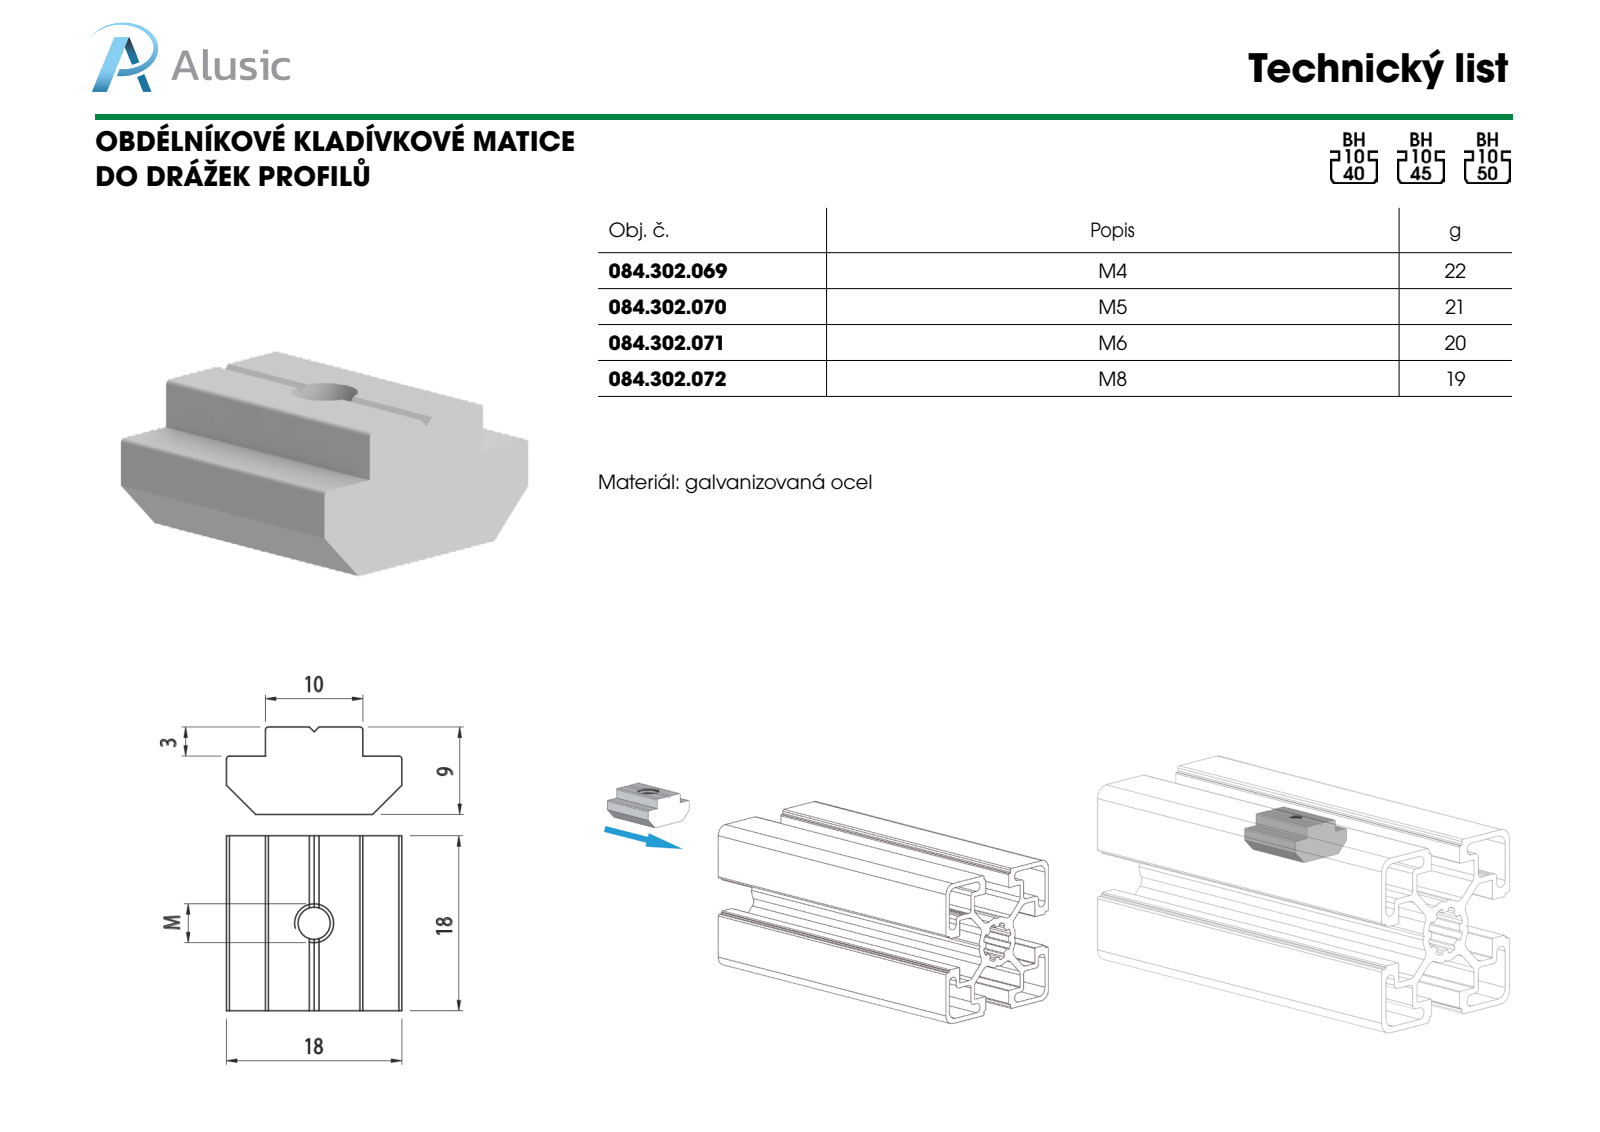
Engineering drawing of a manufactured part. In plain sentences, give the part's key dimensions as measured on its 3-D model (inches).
The part is named "084.302.069". Its 3-D file was written by "SolidWorks 2012 (CONFIG_CONTROL_DESIGN)". It is 1 solid with 23 faces: 17 planar, 6 cylindrical and 0 other. Overall it measures 0.709 by 0.709 by 0.354 inches. Its volume is 0.128 cubic inches and its surface area 1.877 square inches. Round holes: 1 of diameter 0.13. Partial cylindrical surfaces (rounded edges, fillets, slot ends): 4 of radius 0.008. The main face-to-face distances are 0.709, 0.354, 0.236, 0.118, 0.161, 0.547, 0.386, 0.376.
